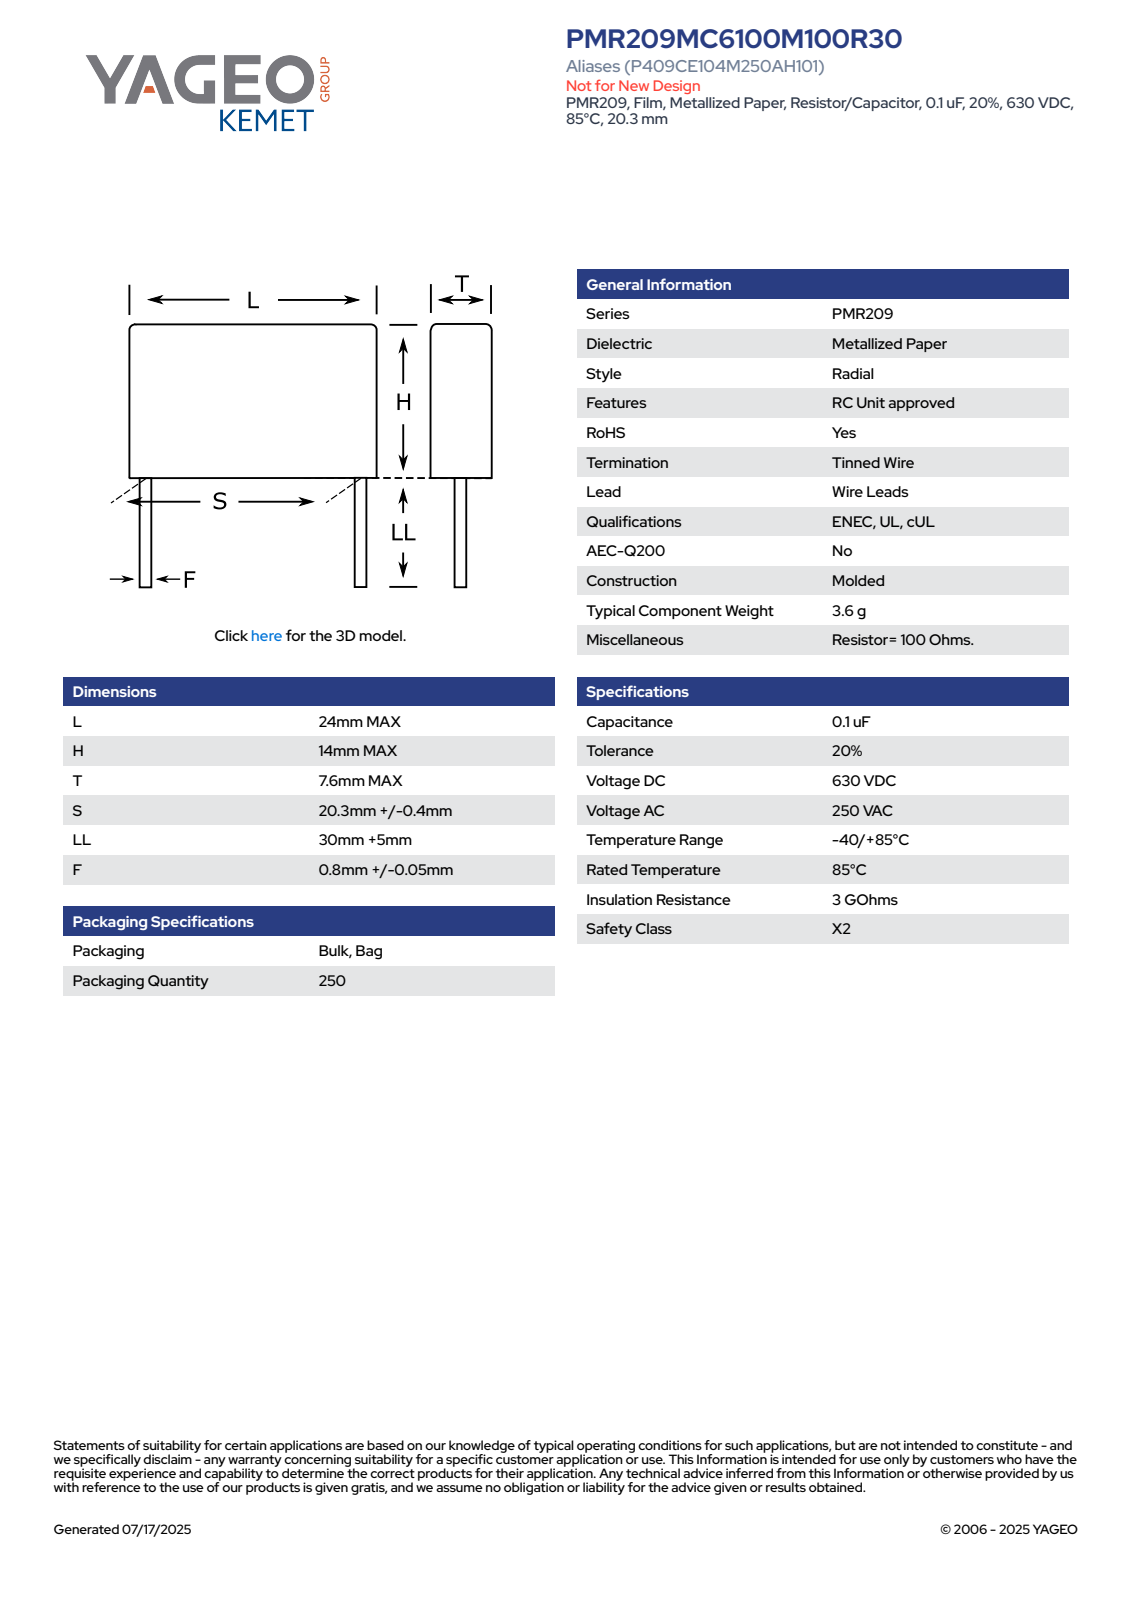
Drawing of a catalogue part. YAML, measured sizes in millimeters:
part_name: "CFR_MOLDED_24X14X7.6_L24H14T7.6S20.3LL35F0.85"
step_written_by: "SolidWorks 2014 (AUTOMOTIVE_DESIGN)"
units: millimeters
bodies: {solids: 4, faces: 73, planar: 65, cylindrical: 8, other: 0}
overall_size: [49, 24, 7.61]
volume: 2590
surface_area: 1451
round_bosses_or_shafts:
  - {diameter: 0.85, count: 2}
partial_cylinders:
  - {radius: 0.5, count: 4}
face_to_face_distances: [7.6, 14, 24, 35, 49, 5.87, 43.02, 8.02, 5.98, 40.87]
